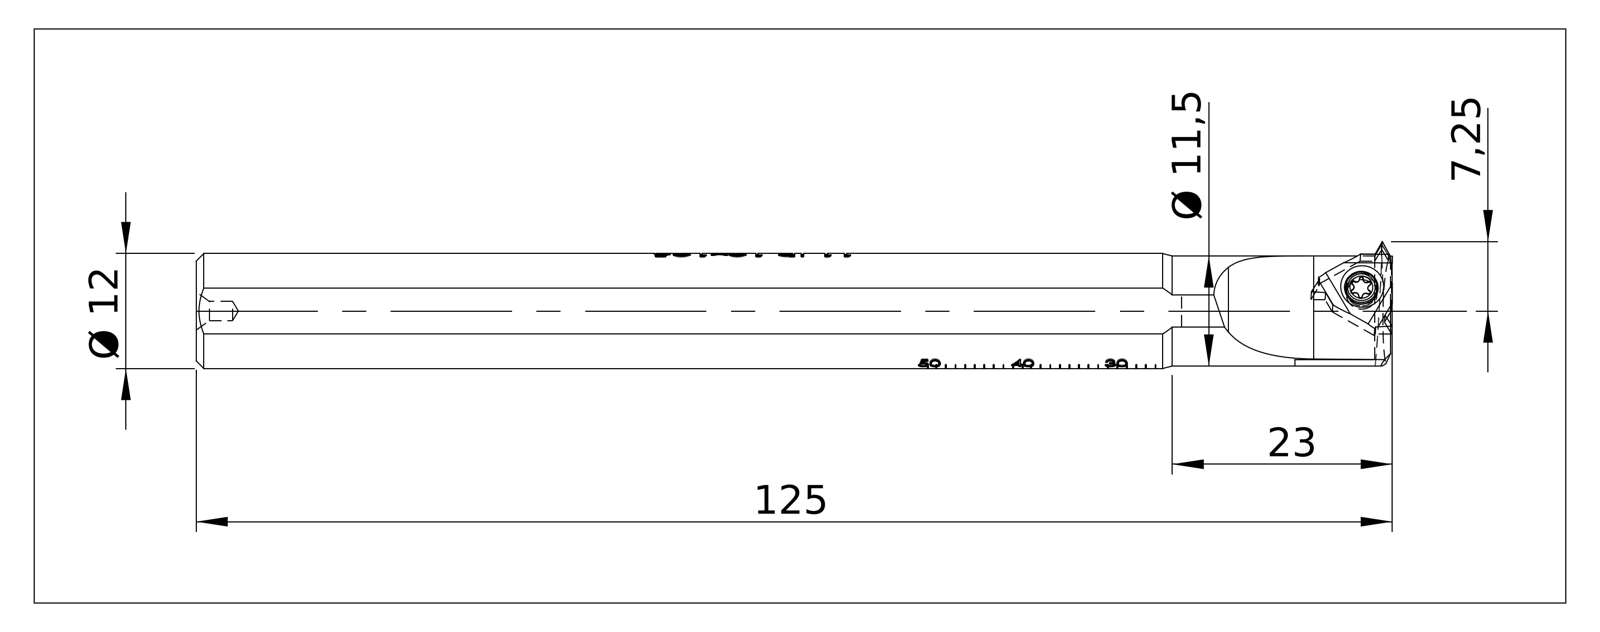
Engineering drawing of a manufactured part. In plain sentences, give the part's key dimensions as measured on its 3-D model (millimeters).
The part is named "CUT; CL-11IR 12x125; NOCUT". Its 3-D file was written by "SolidWorks 2020 (AUTOMOTIVE_DESIGN)". It is 2 solids with 392 faces: 236 planar, 69 cylindrical and 87 other. Overall it measures 125 by 13.25 by 12.04 millimeters. Its volume is 13 121 cubic millimeters and its surface area 5 011 square millimeters. Round holes: 1 of diameter 2, 1 of diameter 3.2. Round bosses or shafts: 1 of diameter 11.5. Partial cylindrical surfaces (rounded edges, fillets, slot ends): 6 of radius 0.16, 6 of radius 0.32, 3 of radius 1, 1 of radius 5.9, 1 of radius 6, 1 of radius 6.38, 1 of radius 15. The main face-to-face distances are 11, 2.6, 3.18, 0.58, 3.67, 7.86, 4.18, 3.68, 4.19, 7.85.
